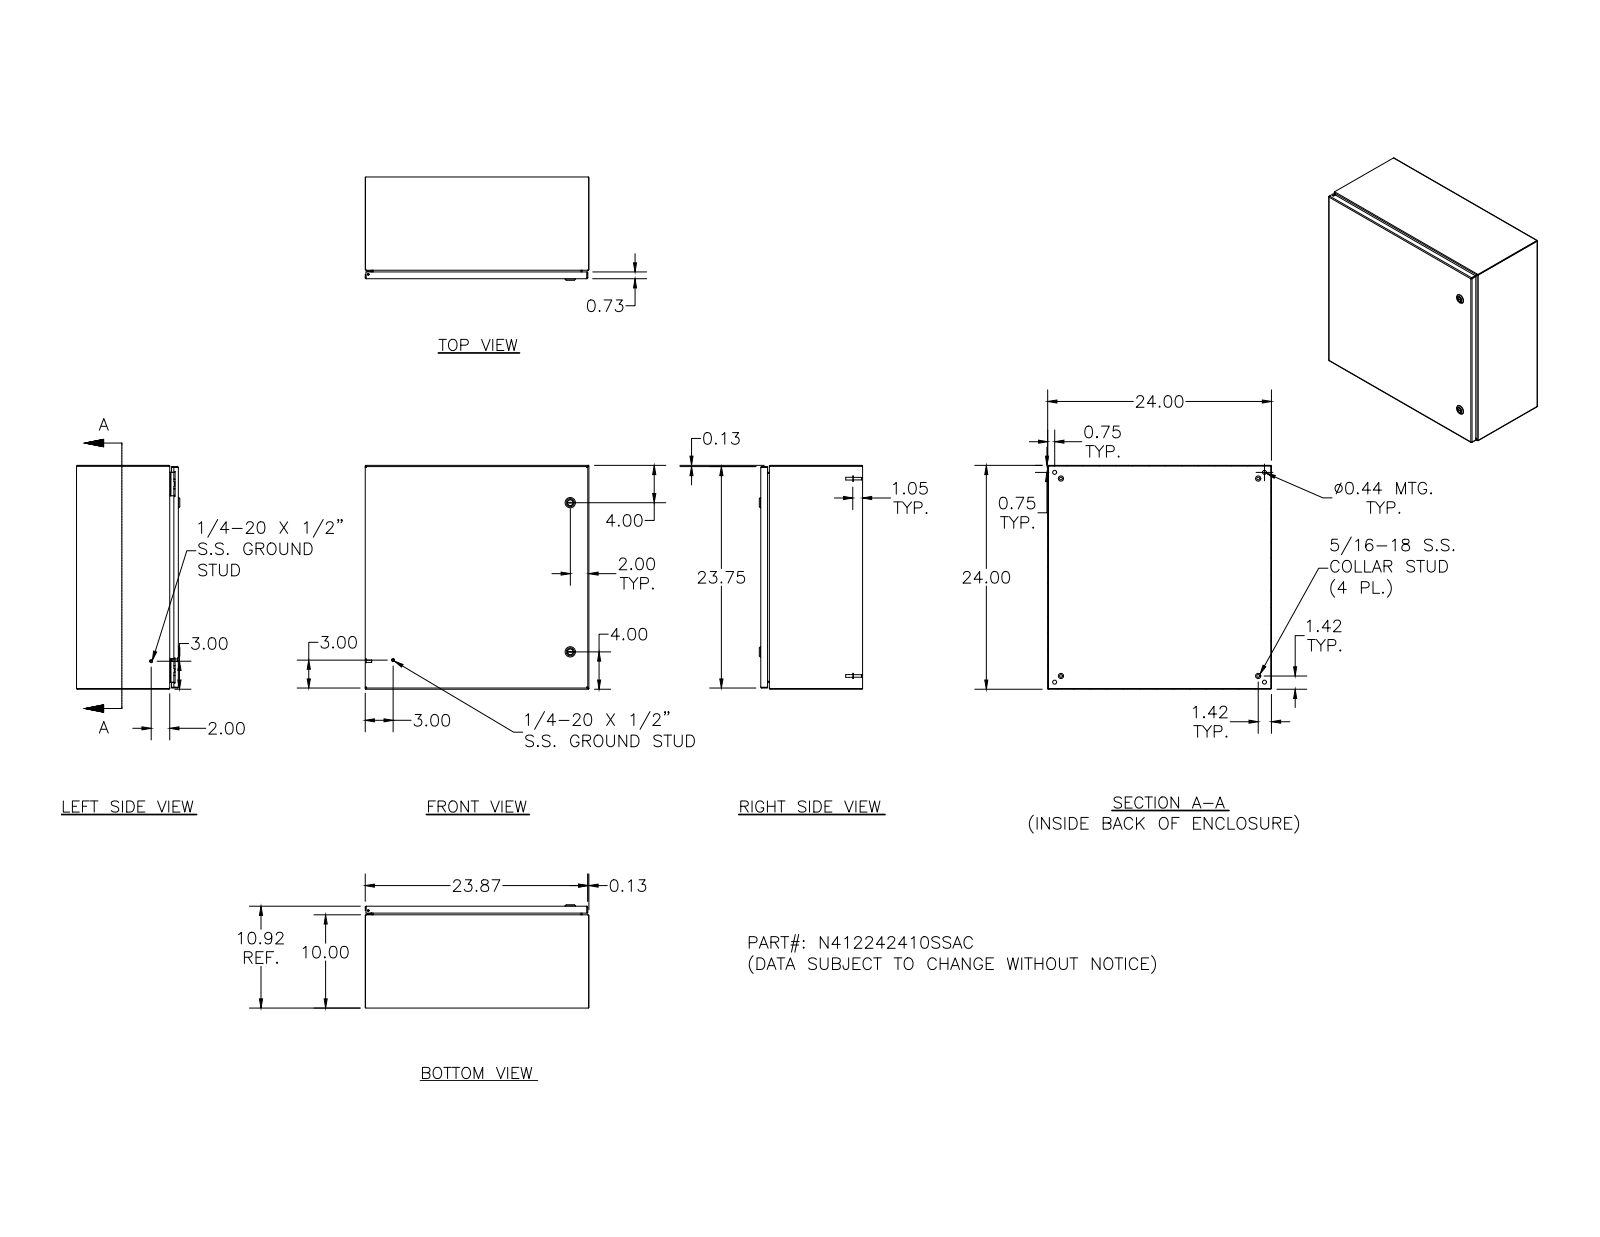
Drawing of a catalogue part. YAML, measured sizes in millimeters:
part_name: "N412242410SSAC; N412242410SSACBKP; 388151; N4122424SSACLID (+8 more)"
step_written_by: "Autodesk Inventor 2011 (AUTOMOTIVE_DESIGN)"
units: millimeters
bodies: {solids: 42, faces: 1662, planar: 698, cylindrical: 588, other: 376}
overall_size: [609.6, 609.6, 281.3]
volume: 2805000
surface_area: 2997000
round_holes:
  - {diameter: 4.8, count: 5}
  - {diameter: 2.4, count: 4}
  - {diameter: 3.9, count: 4}
  - {diameter: 4.2, count: 4}
  - {diameter: 4.4, count: 4}
  - {diameter: 11.1, count: 4}
  - {diameter: 4, count: 2}
  - {diameter: 5, count: 2}
  - {diameter: 8, count: 2}
  - {diameter: 10, count: 2}
  - {diameter: 10.2, count: 2}
  - {diameter: 16.1, count: 2}
round_bosses_or_shafts:
  - {diameter: 6.4, count: 10}
  - {diameter: 14.3, count: 4}
  - {diameter: 9.1, count: 4}
  - {diameter: 8.1, count: 4}
  - {diameter: 7.6, count: 4}
  - {diameter: 7, count: 4}
  - {diameter: 6.5, count: 4}
  - {diameter: 4.2, count: 4}
partial_cylinders:
  - {radius: 1.3, count: 26}
  - {radius: 0.4, count: 18}
  - {radius: 0.4, count: 16}
  - {radius: 2.3, count: 16}
  - {radius: 0.5, count: 15}
  - {radius: 0.8, count: 14}
  - {radius: 3.2, count: 14}
  - {radius: 0.8, count: 8}
face_to_face_distances: [1.9, 275.4, 607.7, 277.3, 273.5, 605.8, 609.6, 252.1, 23.3, 18.8]
hole_center_spacings: [508, 0.4, 16.8, 571.5, 580.9, 0.5, 12.7, 16.5]
